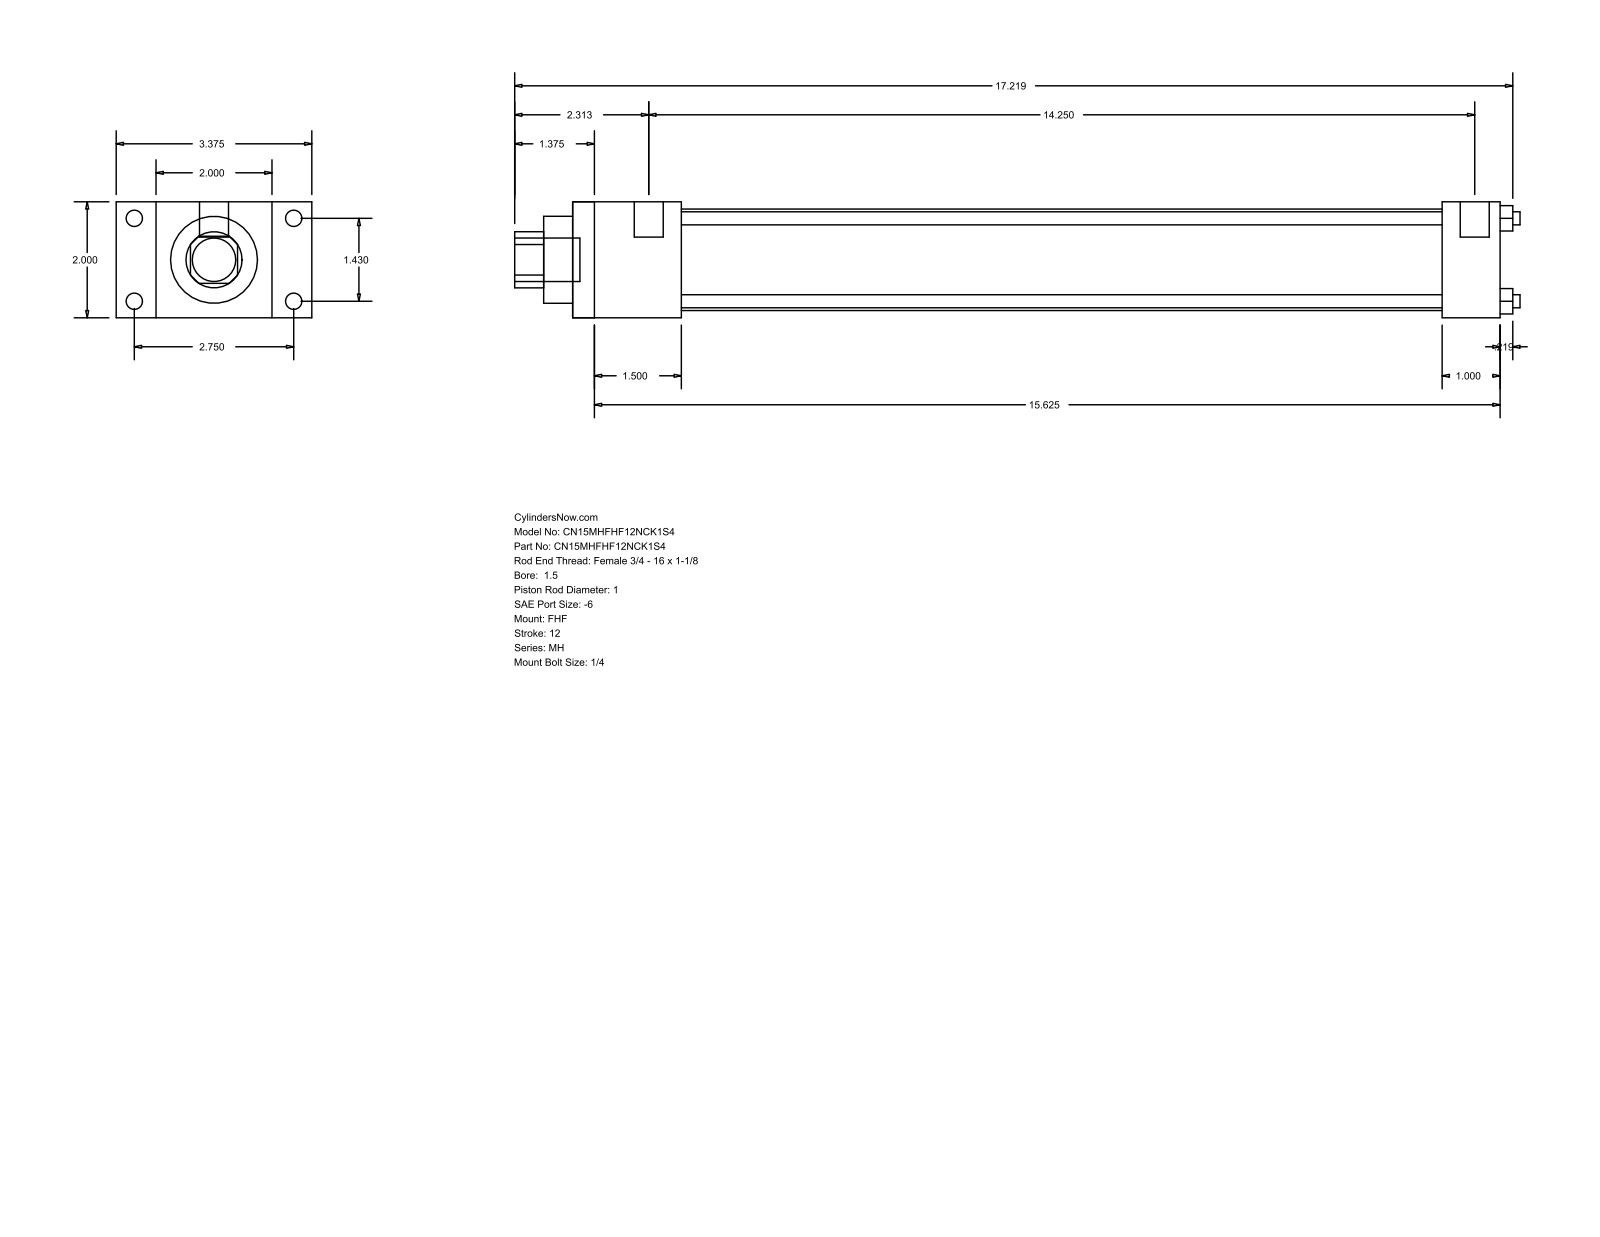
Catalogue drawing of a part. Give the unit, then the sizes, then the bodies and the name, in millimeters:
Units: millimetres
Overall size (bounding box): 440.53 × 85.72 × 50.8
Round holes (diameter × count): ⌀5.71 ×4, ⌀25.4 ×1, ⌀38.1 ×1, ⌀44.45 ×1
Round bosses / shafts (diameter × count): ⌀7.14 ×4, ⌀5.56 ×4, ⌀12.7 ×2, ⌀19.05 ×1
Partial cylindrical surfaces — rounded edges, fillets, slot ends (radius × count): R12.29 ×1
Main face-to-face distances: 50.8, 17.46, 68.26, 47.63, 85.72, 406.4, 358.77, 25.4, 381, 333.37
Hole centre spacings: 25.68, 36.32, 51.36
Bodies: 0 solids, 88 faces (60 planar, 28 cylindrical, 0 other)
Part name (STEP PRODUCT): MH_FHF__0150_1
STEP written by: GSSL Pune (CONFIG_CONTROL_DESIGN)
